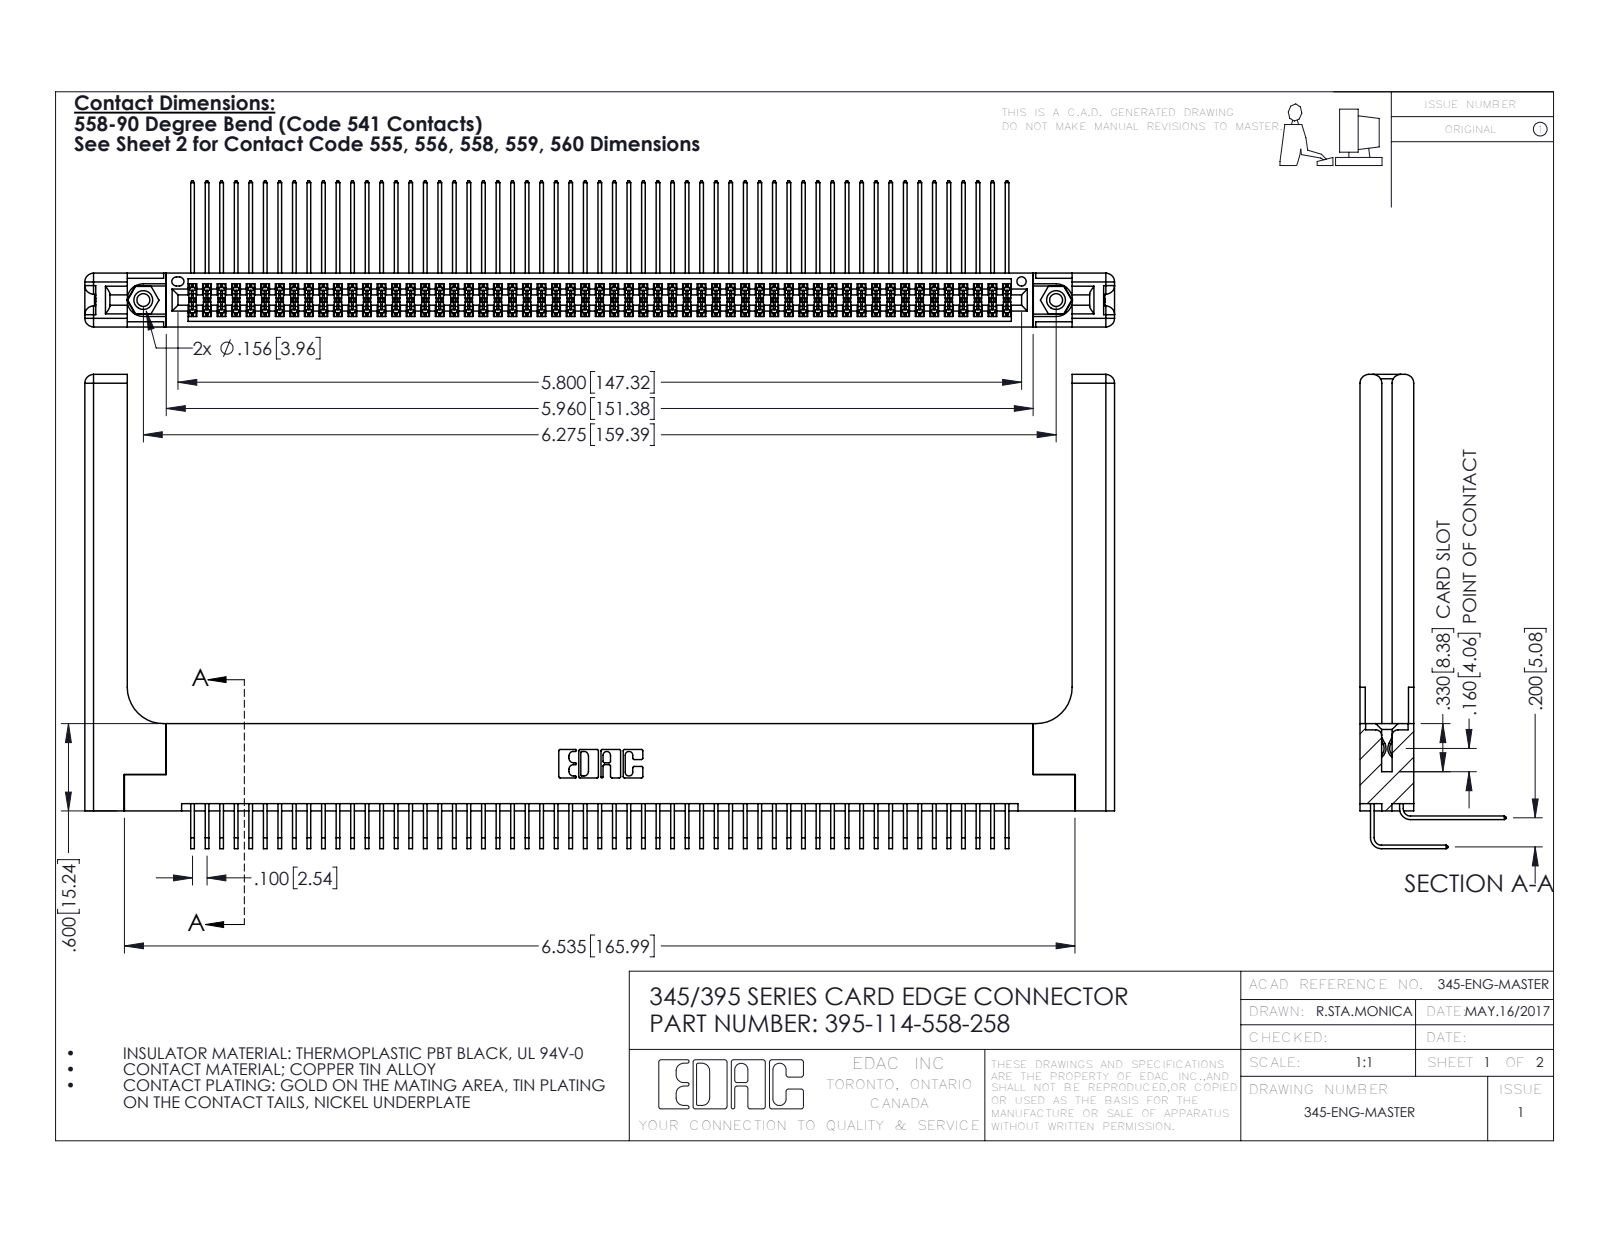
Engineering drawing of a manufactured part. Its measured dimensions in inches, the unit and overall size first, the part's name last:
Units: inches
Overall size (bounding box): 7.079 × 3.259 × 1.005
Round holes (diameter × count): ⌀0.089 ×2, ⌀0.125 ×2, ⌀0.156 ×2, ⌀0.064 ×1
Round bosses / shafts (diameter × count): ⌀0.155 ×2
Partial cylindrical surfaces — rounded edges, fillets, slot ends (radius × count): R0.006 ×171, R0.01 ×22, R0.06 ×16, R0.007 ×6, R0.031 ×6, R0.026 ×3, R0.014 ×2, R0.019 ×2
Main face-to-face distances: 0.072, 0.298, 0.37, 0.2, 0.098, 0.272, 0.025, 0.225, 0.148, 0.15
Hole centre spacings: 0.27, 6.039, 6.275
Volume: 1.632 in³ · Surface area: 54.93 in²
Bodies: 119 solids, 6310 faces (4218 planar, 2032 cylindrical, 60 other)
Part name (STEP PRODUCT): 345 Part_Flush Mounting Lugs - 0.156 Dia-TH; 345-220-058_345-220-058; 395-114-558-258; 345-292-001_558 Tail - 2 (+2 more)
STEP written by: SolidWorks 2016 (CONFIG_CONTROL_DESIGN)
